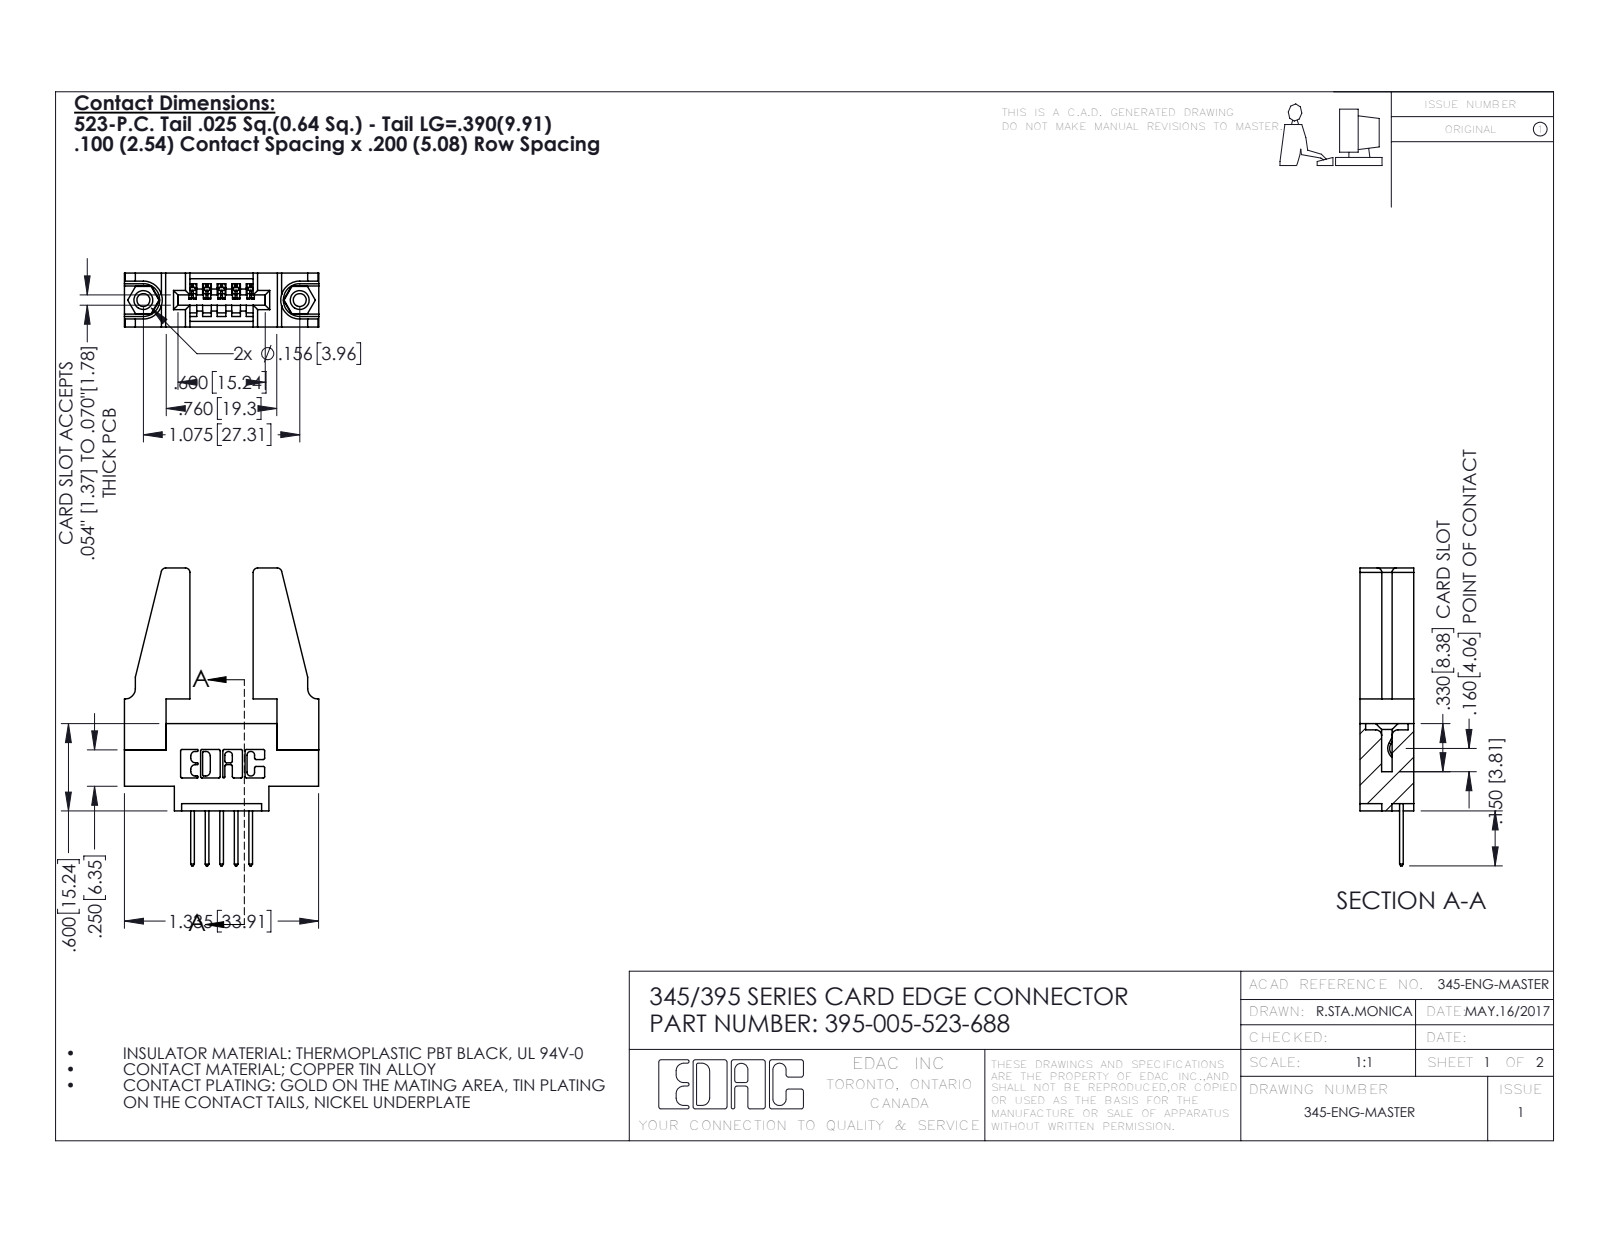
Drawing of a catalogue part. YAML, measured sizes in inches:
part_name: "345-220-078_345-220-088; 345-250-001_345-250-001-102; 345-292-001_345-293-123; 395-005-523-688 (+1 more)"
step_written_by: "SolidWorks 2016 (CONFIG_CONTROL_DESIGN)"
units: inches
bodies: {solids: 10, faces: 544, planar: 356, cylindrical: 172, other: 16}
overall_size: [2.047, 1.336, 0.37]
volume: 0.37
surface_area: 10.05
round_holes:
  - {diameter: 0.089, count: 2}
  - {diameter: 0.125, count: 2}
  - {diameter: 0.156, count: 2}
  - {diameter: 0.064, count: 1}
round_bosses_or_shafts:
  - {diameter: 0.155, count: 2}
partial_cylinders:
  - {radius: 0.01, count: 22}
  - {radius: 0.006, count: 10}
  - {radius: 0.01, count: 10}
  - {radius: 0.03, count: 8}
  - {radius: 0.007, count: 6}
  - {radius: 0.031, count: 6}
  - {radius: 0.026, count: 3}
  - {radius: 0.031, count: 2}
face_to_face_distances: [0.37, 0.072, 0.298, 0.2, 0.148, 0.15, 0.22, 0.077, 0.098, 0.272]
hole_center_spacings: [0.27, 0.847, 1.075]
